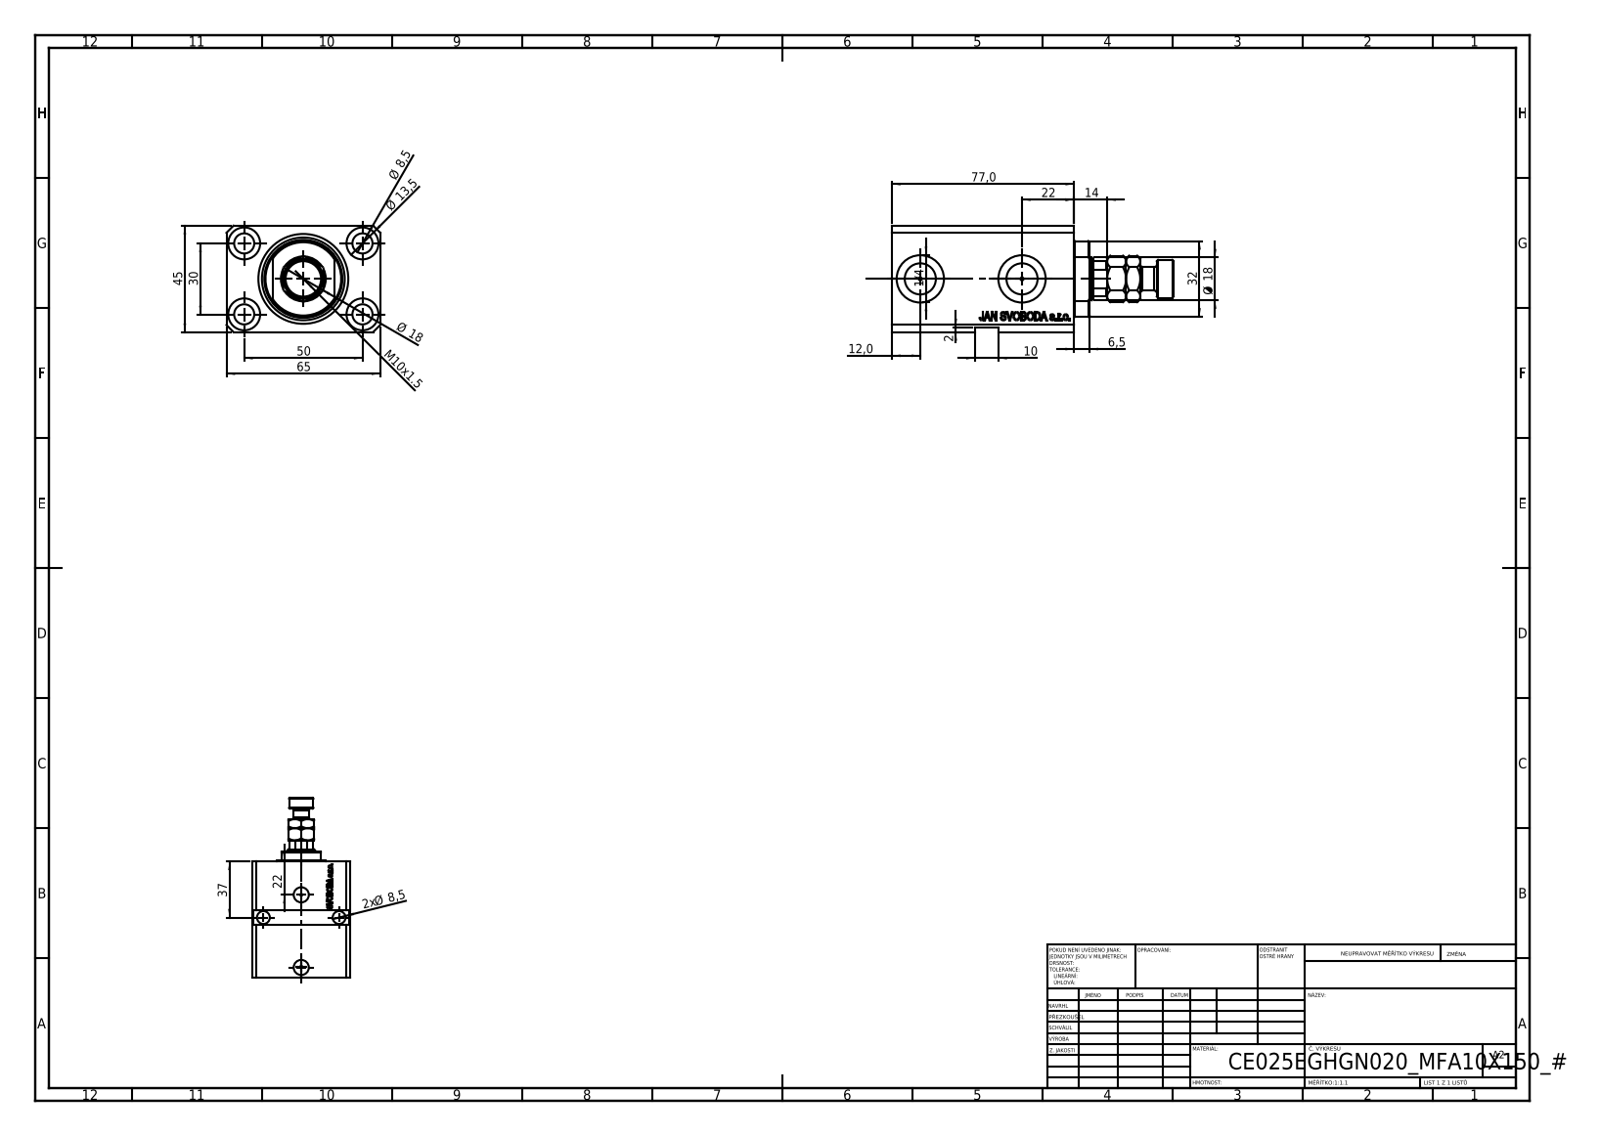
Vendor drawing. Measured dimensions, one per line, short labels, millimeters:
name: V250CE_C_VCP; V250CE_E_Body; V250CE_VC_E; MFA
written by: SolidWorks 2019 (CONFIG_CONTROL_DESIGN)
unit: mm
bodies: 4 solids, 949 faces (451 planar, 88 cylindrical, 410 other)
size: 119 × 65 × 45
volume: 197 140 mm³; area: 54 323 mm²
holes: 7× ⌀8.5, 4× ⌀1.25, 4× ⌀13.5, 2× ⌀10, 2× ⌀13.16, 2× ⌀20, 1× ⌀18, 1× ⌀25, 1× ⌀38
bosses: 1× ⌀16, 1× ⌀10
rounds: 1× R8.5, 1× R16
face distances: 45, 65, 14, 63, 77, 6.9, 56.1, 70.1, 28, 43
hole spacings: 29.15, 50, 30, 40.98, 41.4, 58.31, 0.53, 43
